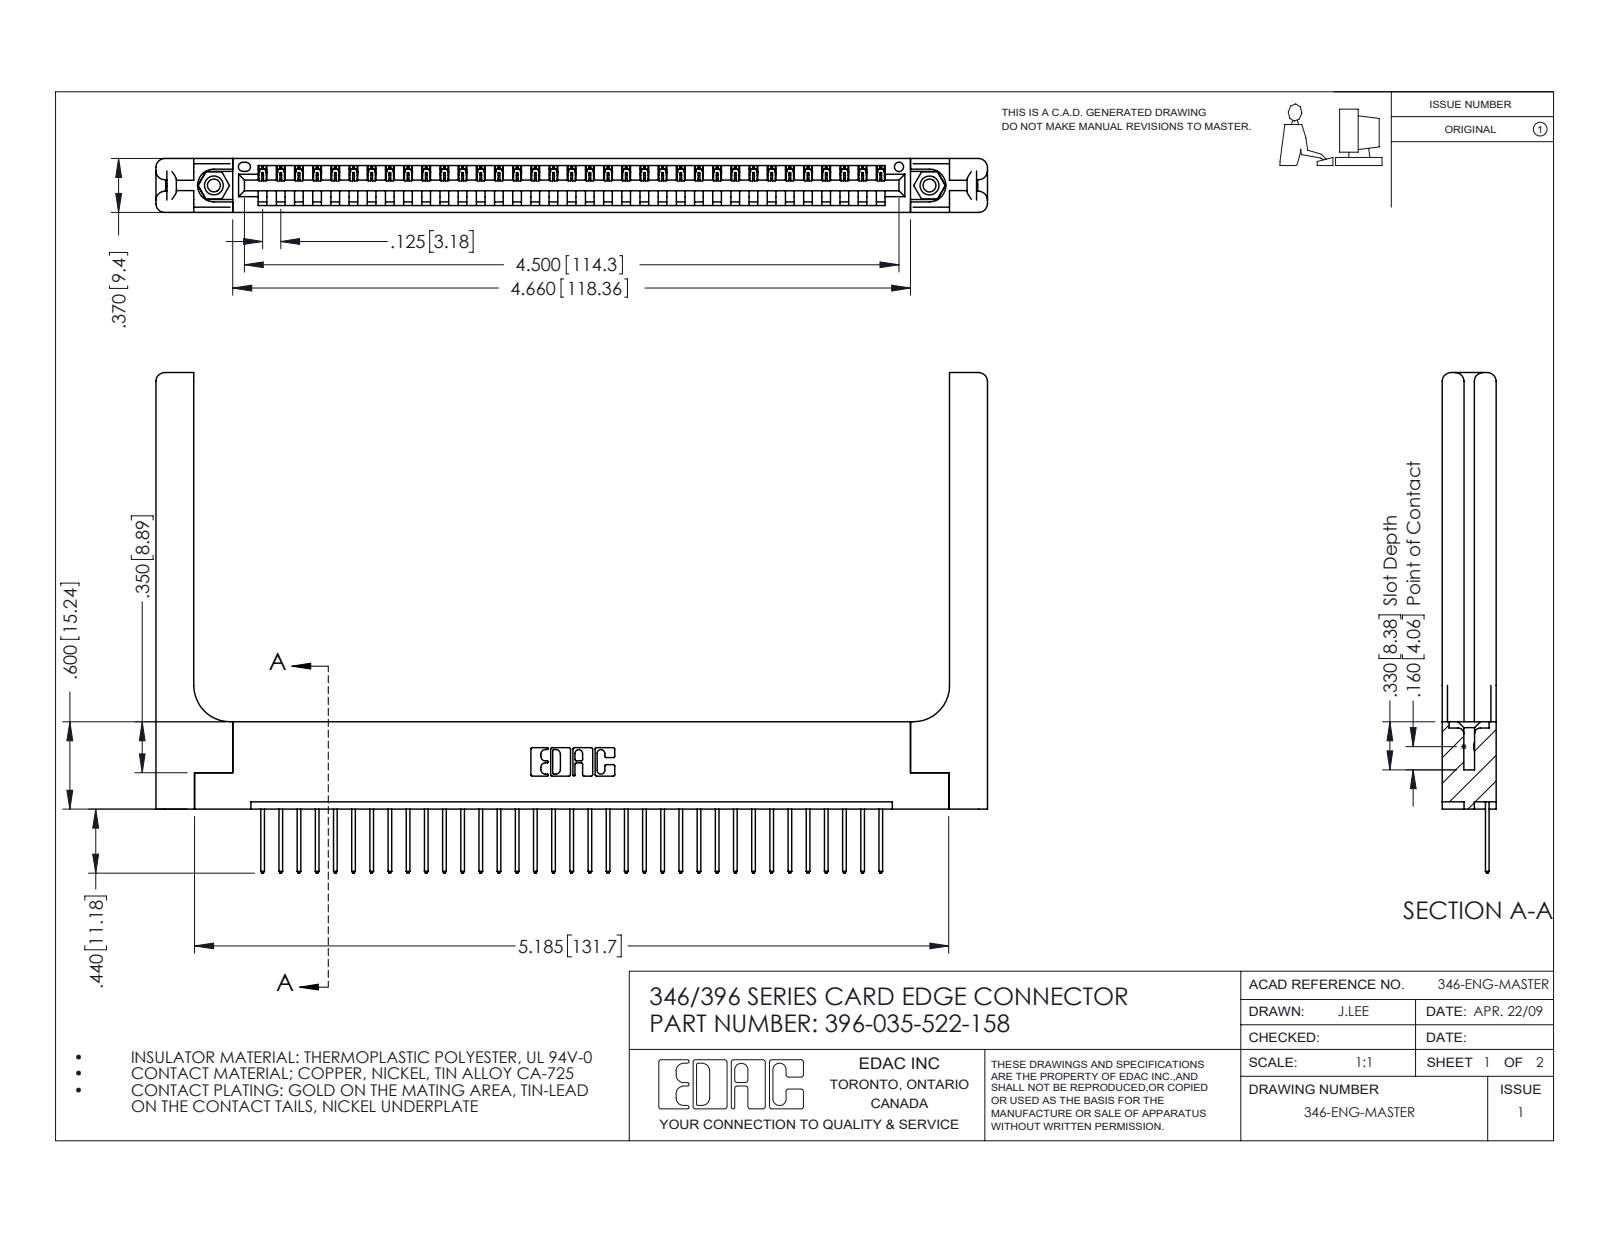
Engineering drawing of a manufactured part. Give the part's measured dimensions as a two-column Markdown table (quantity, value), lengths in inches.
| quantity | value |
| --- | --- |
| part name | 346 Part_Flush Mounting Lugs - 0.156 Dia-TH; 345-292-001_345-293-122; 346-220-058_345-220-058; 396-035-522-158 (+1 more) |
| STEP written by | SolidWorks 2016 (CONFIG_CONTROL_DESIGN) |
| units | inches |
| bodies | 40 solids, 2408 faces (1624 planar, 724 cylindrical, 60 other) |
| overall size | 5.716 × 3.44 × 0.37 |
| volume | 1.304 in³ |
| surface area | 34.93 in² |
| round holes (diameter × count) | 0.089 × 2, 0.125 × 2, 0.156 × 2, 0.064 × 1 |
| round bosses / shafts (diameter × count) | 0.155 × 2 |
| partial cylindrical surfaces (radius × count) | 0.006 × 70, 0.01 × 70, 0.01 × 22, 0.06 × 16, 0.007 × 6, 0.031 × 6, 0.026 × 3, 0.03 × 2 |
| main face-to-face distances | 0.37, 0.048, 0.322, 0.072, 0.148, 0.15, 0.25, 0.298, 0.025, 0.222 |
| hole center spacings | 0.246, 4.711, 4.92 |
